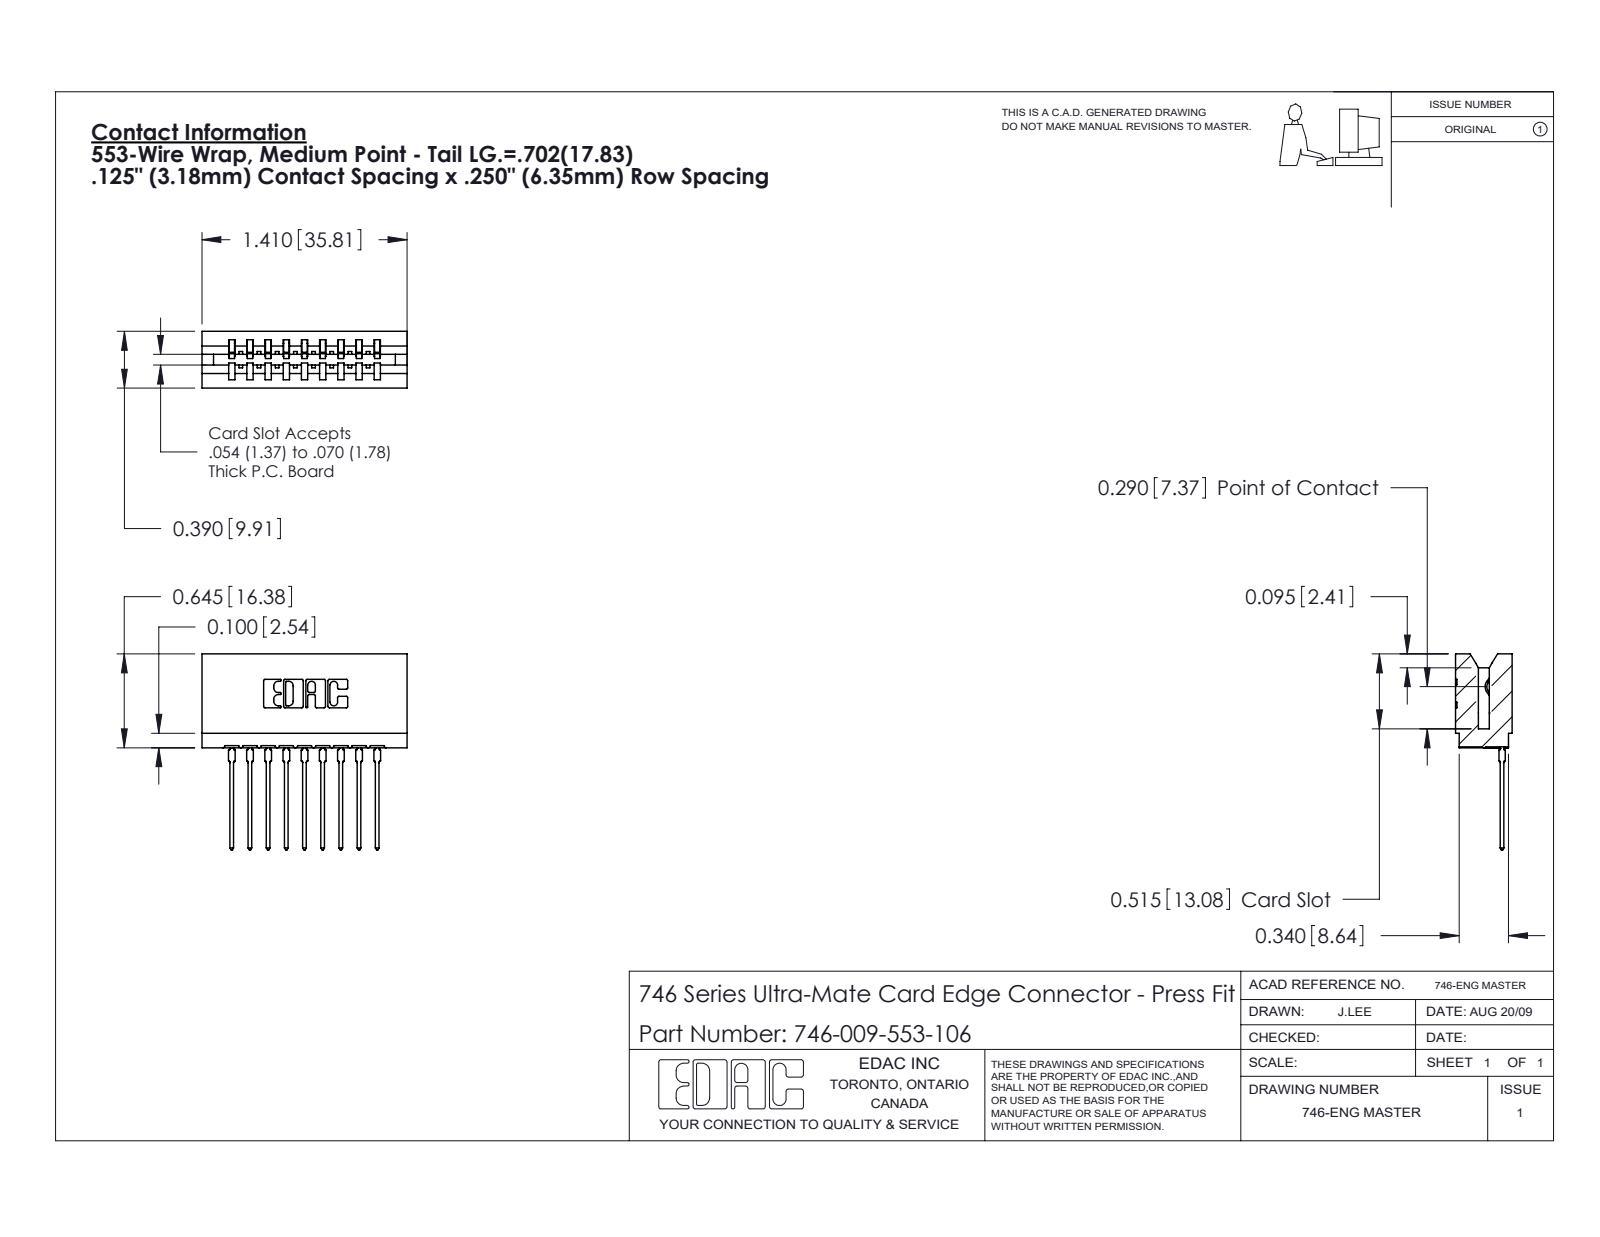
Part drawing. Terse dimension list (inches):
name: 746-009-553-106; 746 Part_.515 Slot Depth - 06; 746-292-001_553
written by: SolidWorks 2020 (CONFIG_CONTROL_DESIGN)
unit: in
bodies: 10 solids, 1070 faces (623 planar, 213 cylindrical, 234 other)
size: 1.41 × 1.346 × 0.39
volume: 0.243 in³; area: 8.562 in²
rounds: 22× R0.01, 18× R0.021, 10× R0.015, 6× R0.007, 6× R0.031, 4× R0.005, 4× R0.011, 3× R0.026
face distances: 0.25, 0.5, 0.333, 0.042, 0.125, 0.125, 0.057, 0.292, 0.208, 0.083
